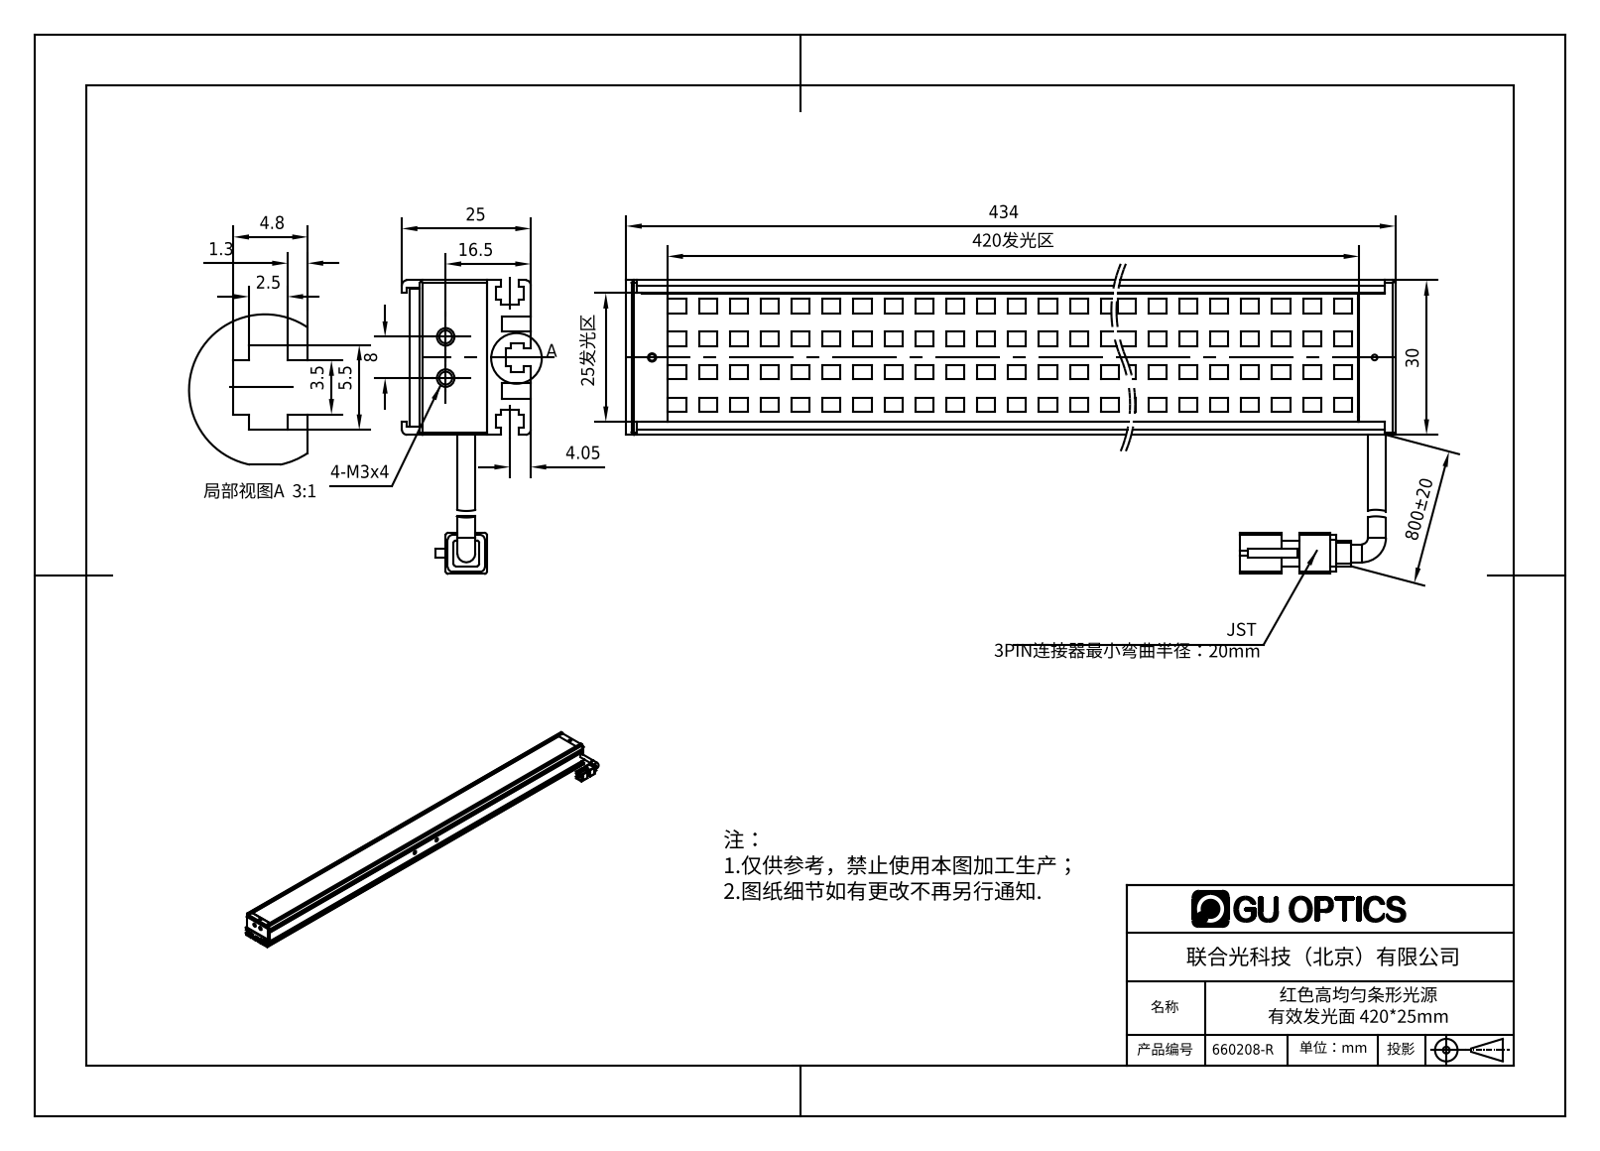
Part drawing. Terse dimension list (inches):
name: 660208
written by: SolidWorks 2016 (AUTOMOTIVE_DESIGN)
unit: in
bodies: 6 solids, 1842 faces (1656 planar, 83 cylindrical, 103 other)
size: 17.087 × 2.244 × 0.984
volume: 8.864 in³; area: 230.2 in²
holes: 5× ⌀0.063, 2× ⌀0.059, 2× ⌀0.067, 2× ⌀0.098, 2× ⌀0.11, 2× ⌀0.118, 1× ⌀0.043, 1× ⌀0.049, 1× ⌀0.079
bosses: 2× ⌀0.138
rounds: 12× R0.039, 8× R0.02, 1× R0.065
face distances: 0.039, 0.079, 0.512, 0.098, 0.118, 1.083, 0.374, 0.177, 0.472, 0.594
hole spacings: 16.732, 0.276, 16.735, 0.315, 1.181, 7.756, 7.76, 7.795
